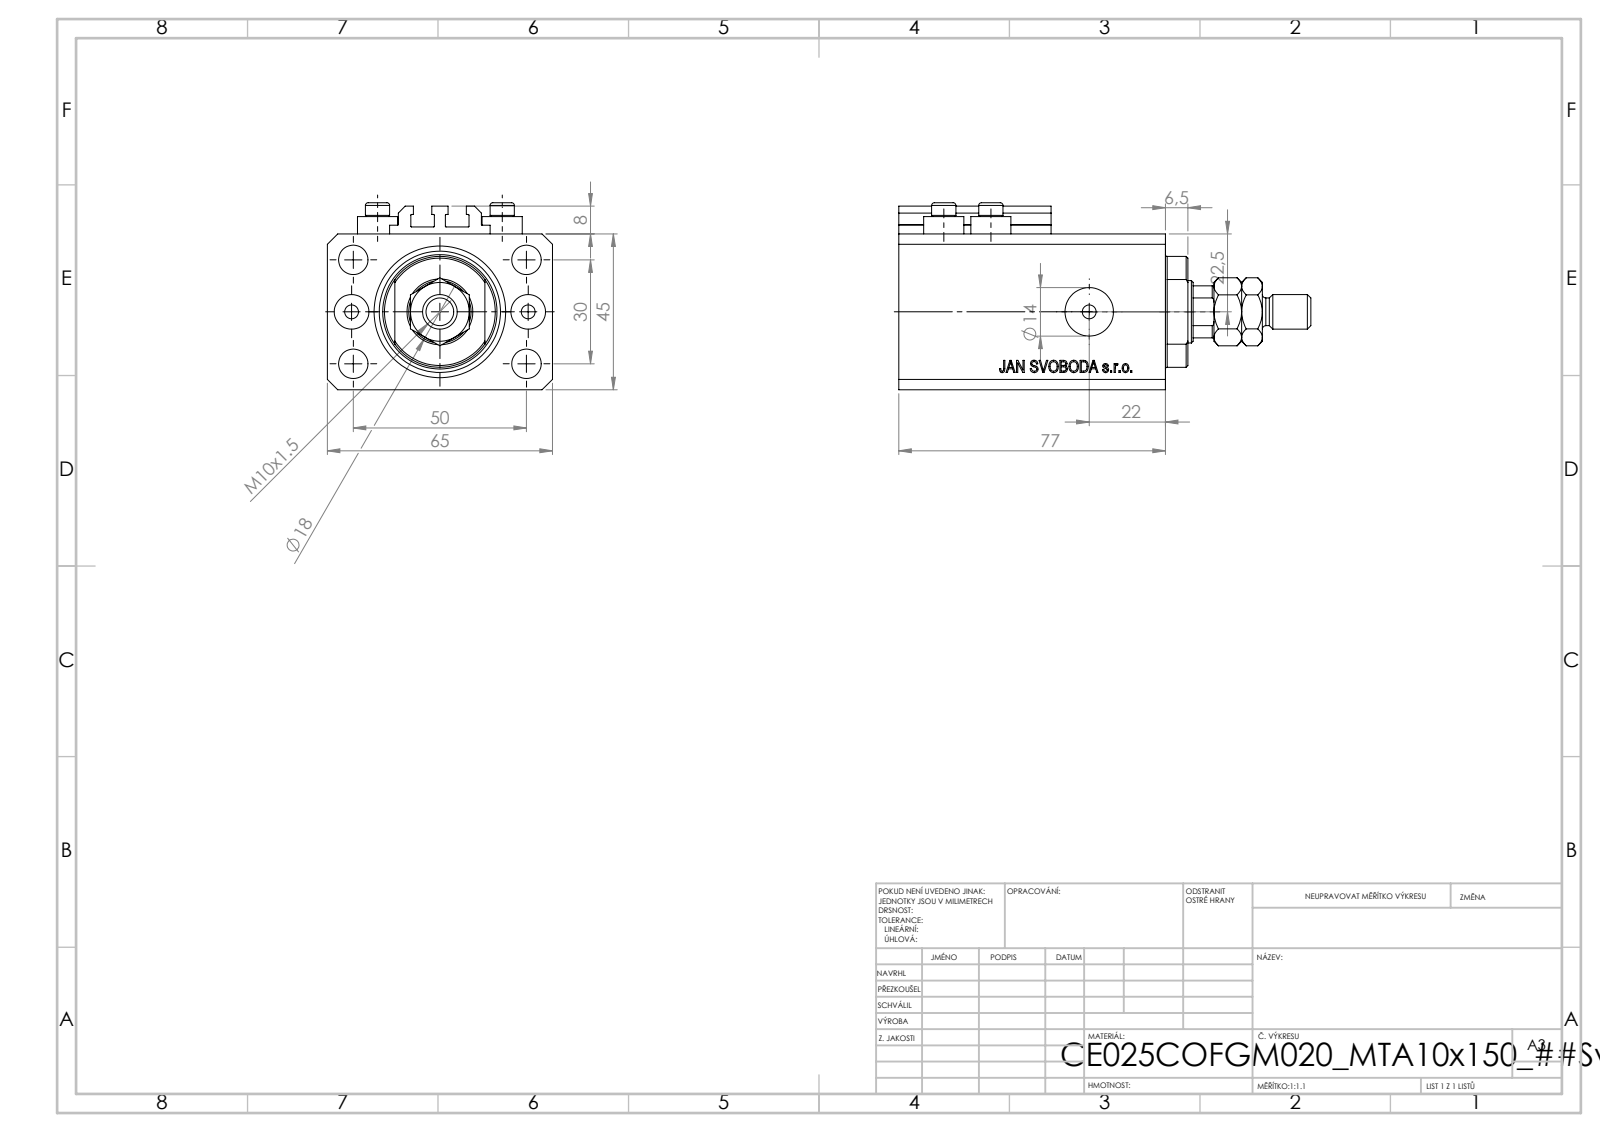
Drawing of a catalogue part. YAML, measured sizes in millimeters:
part_name: "MTA; ALLEN BOLT V250CE; V250CE_C_VCP; V250CE_C_Body (+1 more)"
step_written_by: "SolidWorks 2019 (CONFIG_CONTROL_DESIGN)"
units: millimeters
bodies: {solids: 9, faces: 1083, planar: 519, cylindrical: 90, other: 474}
overall_size: [119, 65, 54]
volume: 216425
surface_area: 59004
round_holes:
  - {diameter: 4, count: 8}
  - {diameter: 8.5, count: 5}
  - {diameter: 10, count: 2}
  - {diameter: 14, count: 2}
  - {diameter: 18, count: 1}
  - {diameter: 25, count: 1}
  - {diameter: 38, count: 1}
round_bosses_or_shafts:
  - {diameter: 11.6, count: 4}
  - {diameter: 7, count: 4}
  - {diameter: 10, count: 1}
  - {diameter: 8, count: 1}
partial_cylinders:
  - {radius: 0.2, count: 10}
  - {radius: 8.5, count: 1}
  - {radius: 16, count: 1}
face_to_face_distances: [45, 65, 14, 63, 77, 6.9, 56.1, 70.1, 20.5, 3]
hole_center_spacings: [15.01, 29.15, 52.68, 13.6, 25.5, 30, 36, 38.48]
